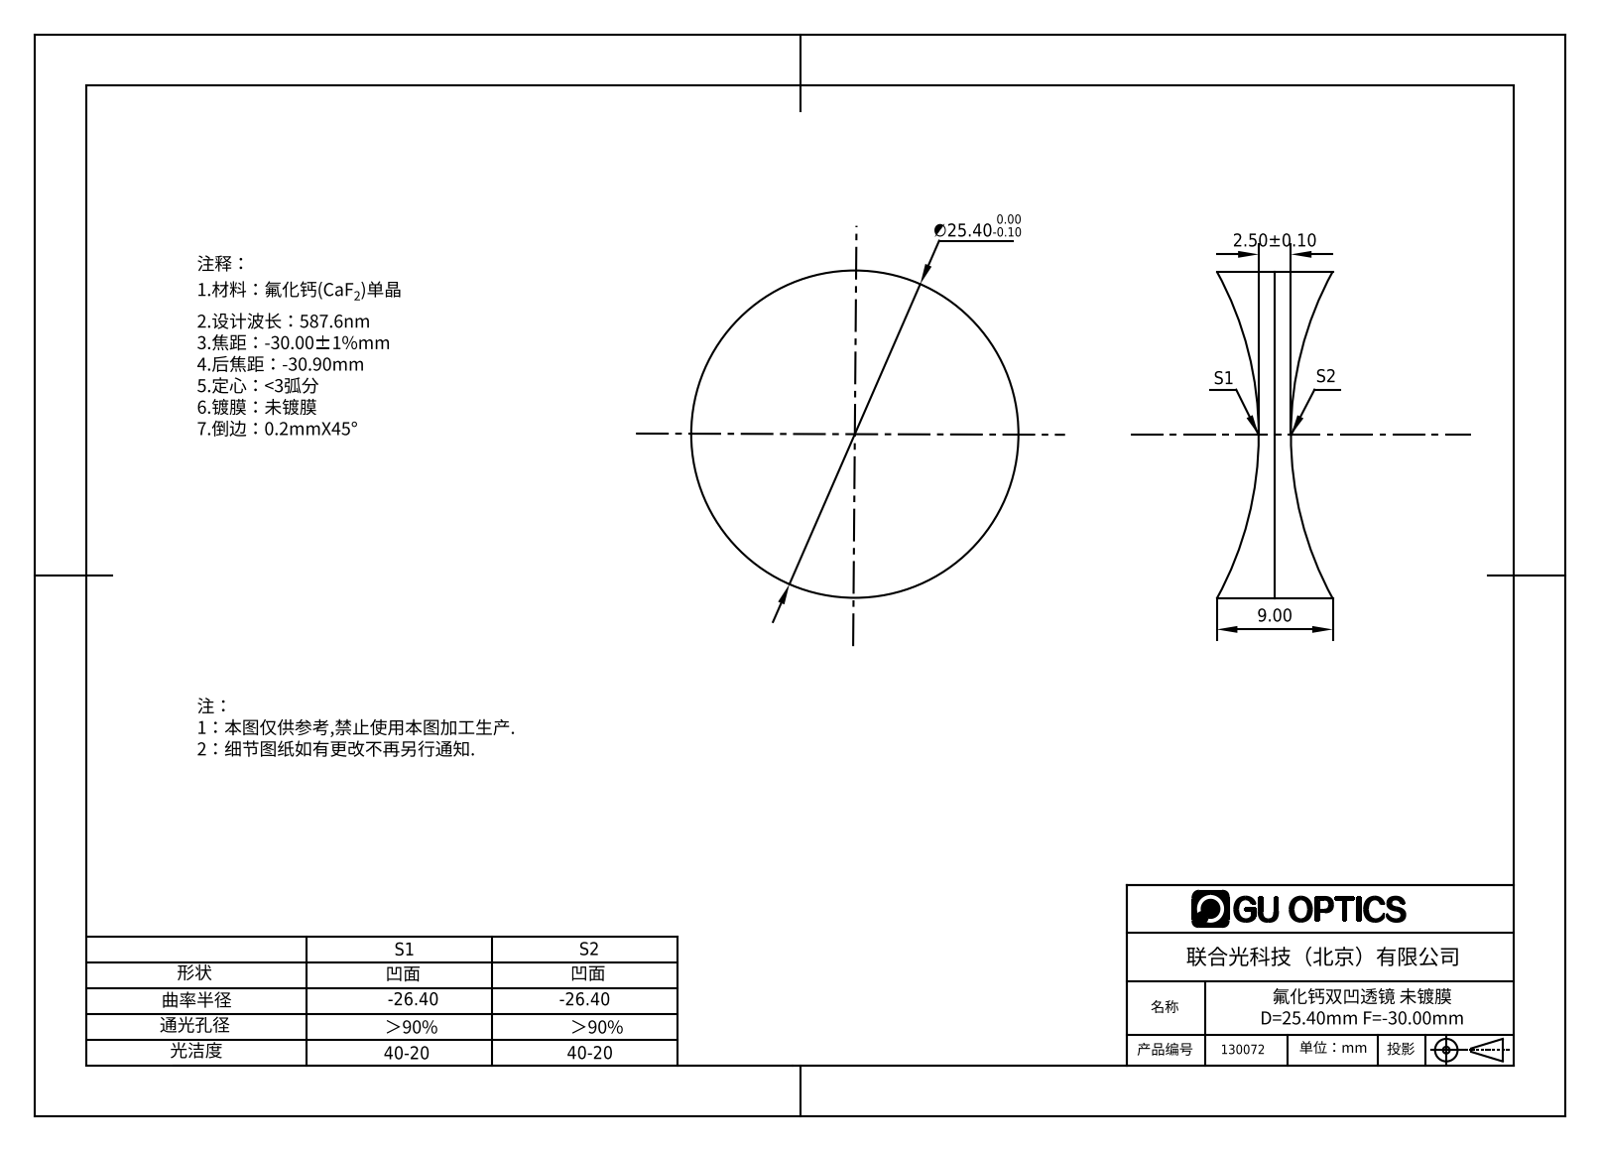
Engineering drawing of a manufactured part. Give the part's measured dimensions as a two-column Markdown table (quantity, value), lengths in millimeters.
| quantity | value |
| --- | --- |
| part name | 130072 |
| STEP written by | SolidWorks 2016 (AUTOMOTIVE_DESIGN) |
| units | millimeters |
| bodies | 1 solid, 6 faces (0 planar, 2 cylindrical, 4 other) |
| overall size | 25.4 × 25.4 × 9.01 |
| volume | 2 880 mm³ |
| surface area | 1 799 mm² |
| round bosses / shafts (diameter × count) | 25.4 × 1 |
